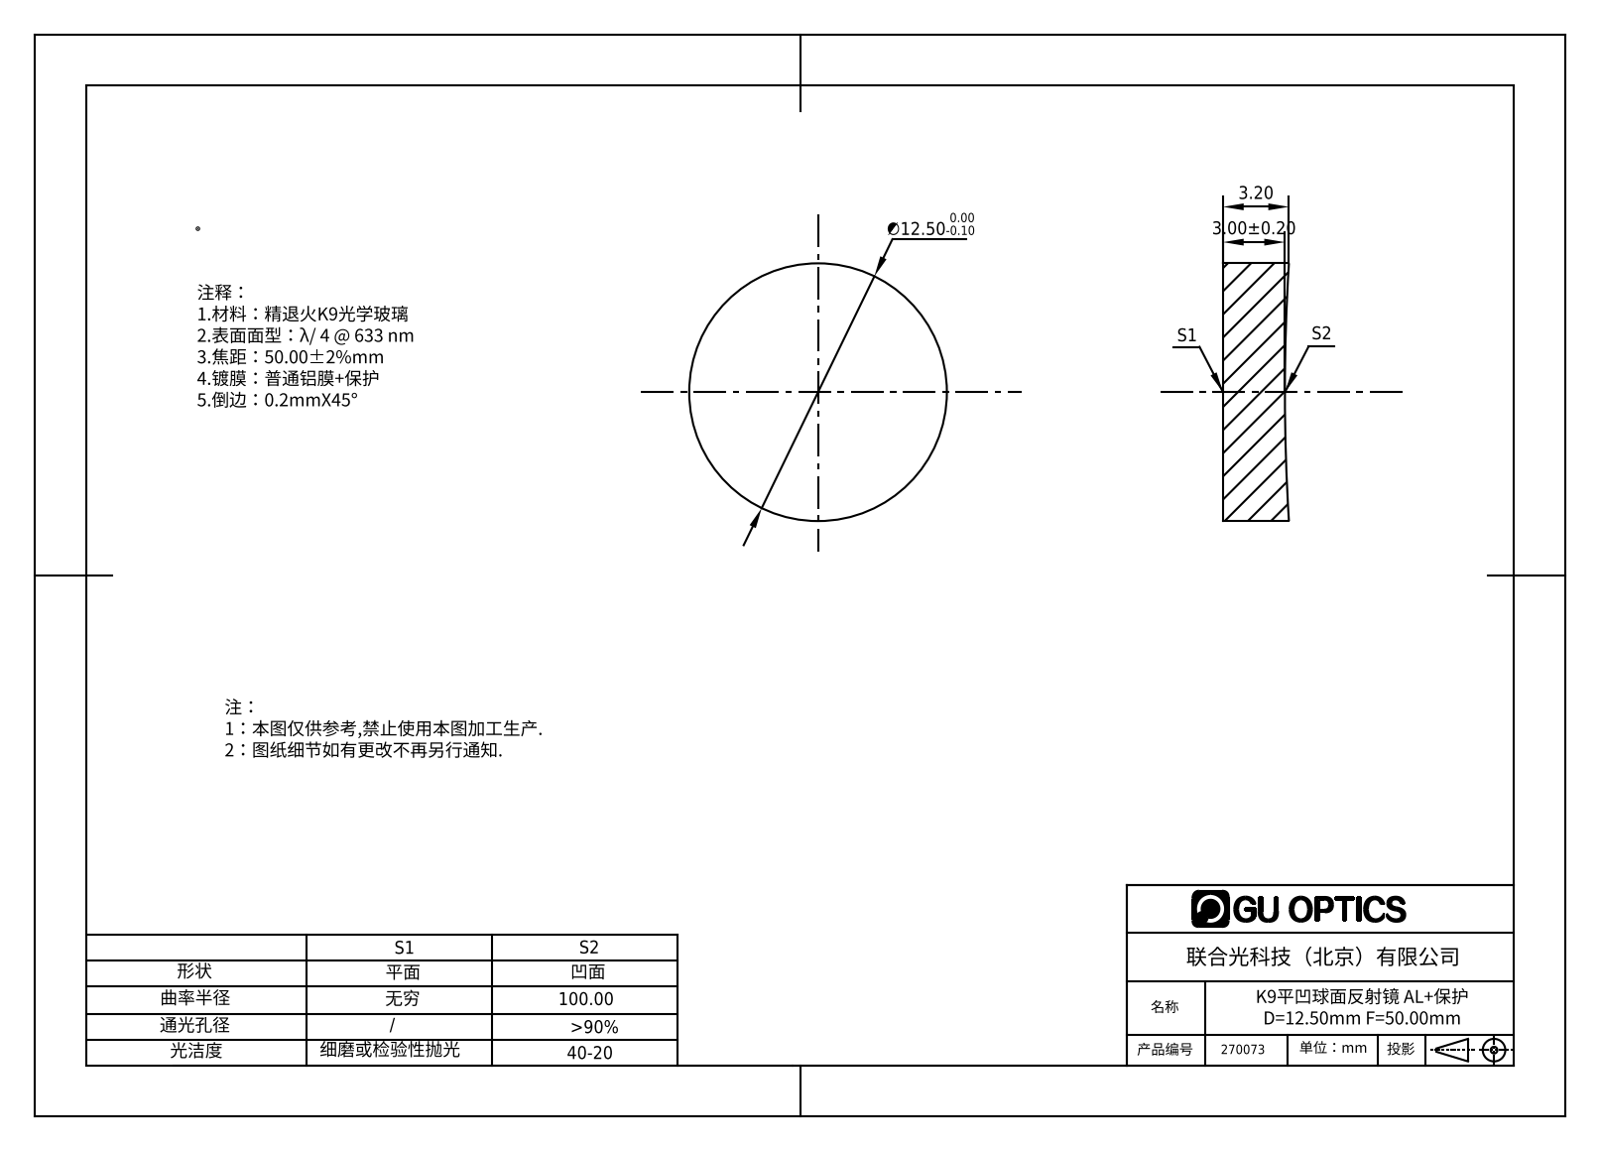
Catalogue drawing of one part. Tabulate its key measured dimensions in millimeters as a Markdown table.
| quantity | value |
| --- | --- |
| part name | 270008 |
| STEP written by | SolidWorks 2016 (AUTOMOTIVE_DESIGN) |
| units | millimeters |
| bodies | 1 solid, 5 faces (1 planar, 2 cylindrical, 2 other) |
| overall size | 12.5 × 12.5 × 3.2 |
| volume | 380 mm³ |
| surface area | 371 mm² |
| round bosses / shafts (diameter × count) | 12.5 × 1 |
